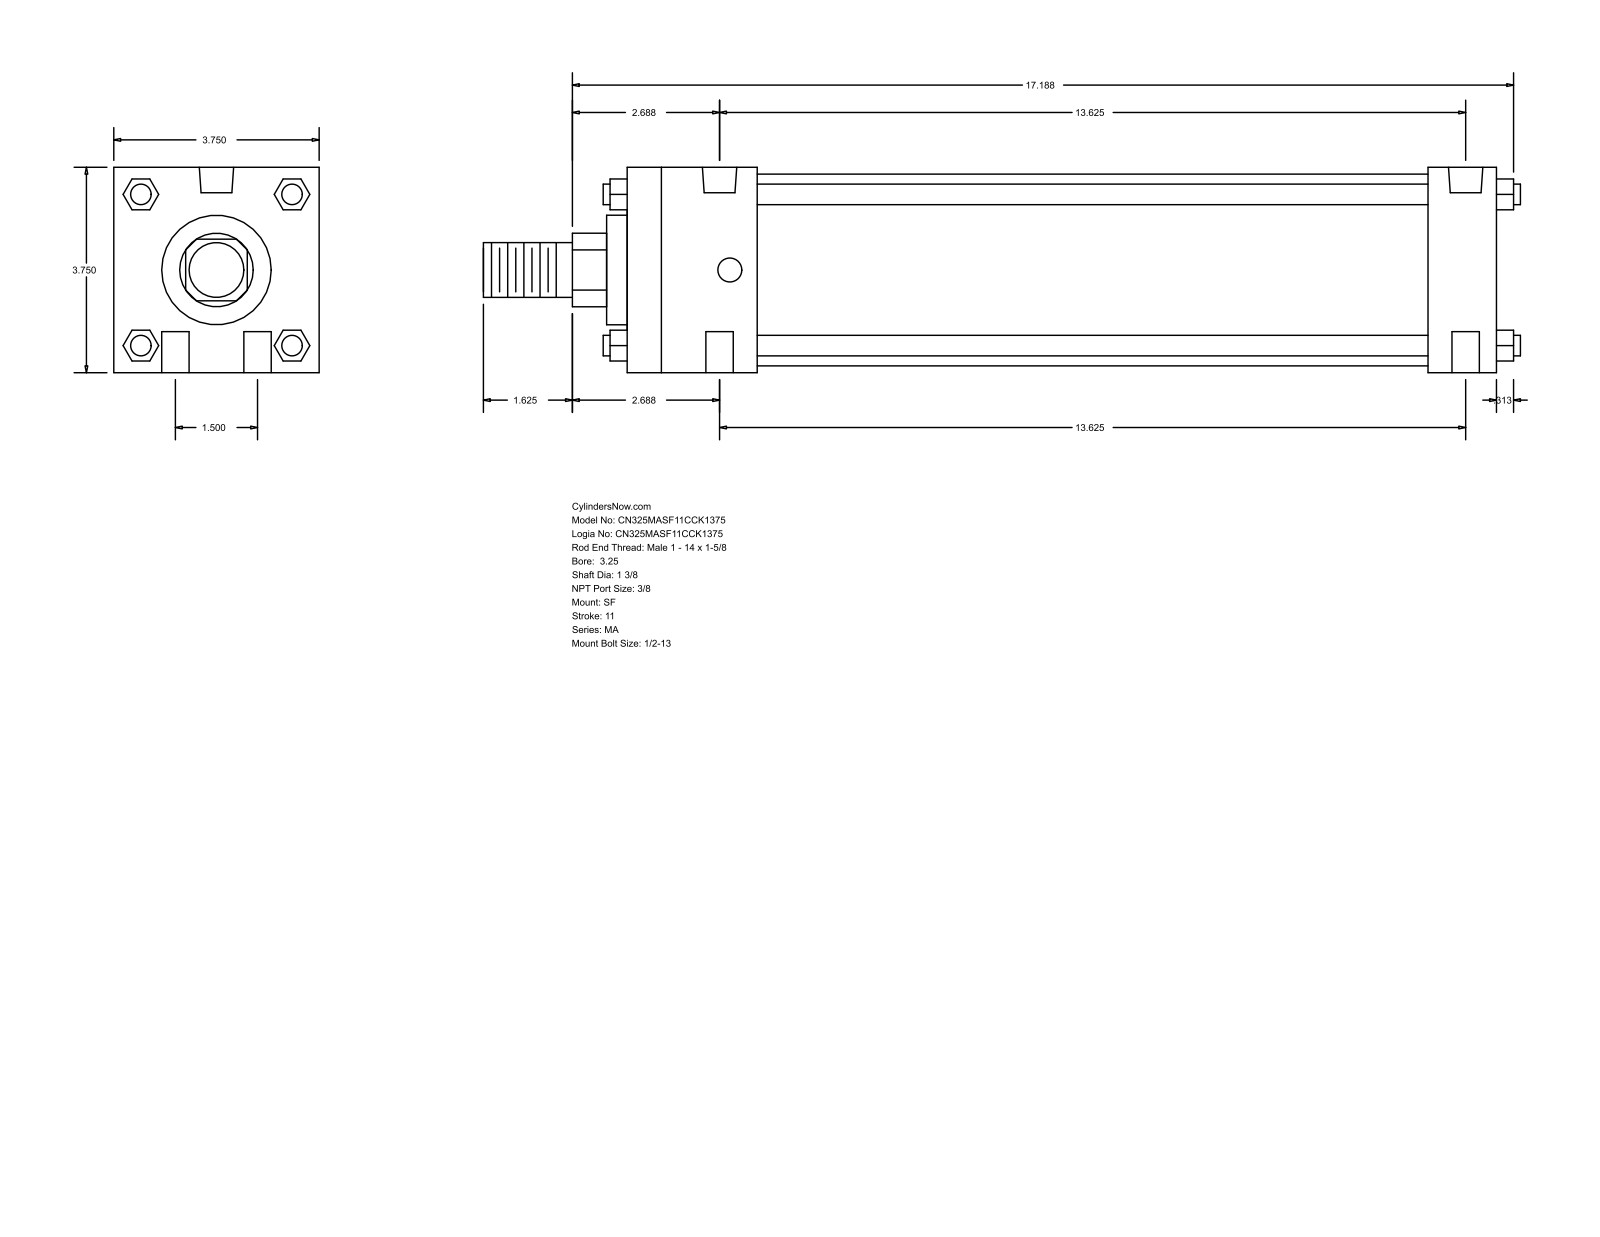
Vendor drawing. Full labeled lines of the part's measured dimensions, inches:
Part name (STEP PRODUCT): MA_SF__0325_1.375
STEP written by: GSSL Pune (CONFIG_CONTROL_DESIGN)
Units: inches
Bodies: 0 solids, 124 faces (94 planar, 30 cylindrical, 0 other)
Overall size (bounding box): 18.937 × 3.75 × 3.75
Round holes (diameter × count): ⌀0.5 ×4, ⌀0.437 ×2, ⌀0.627 ×2
Round bosses / shafts (diameter × count): ⌀0.375 ×4, ⌀3.5 ×1, ⌀2 ×1, ⌀1.375 ×1, ⌀1 ×1
Partial cylindrical surfaces — rounded edges, fillets, slot ends (radius × count): R0.672 ×1
Main face-to-face distances: 3.75, 15.875, 14.625, 1.25, 2.375, 12.25, 13.5, 0.375, 2.75, 15
Hole centre spacings: 0.75, 13.646, 13.625, 1.5, 13.707, 13.25
